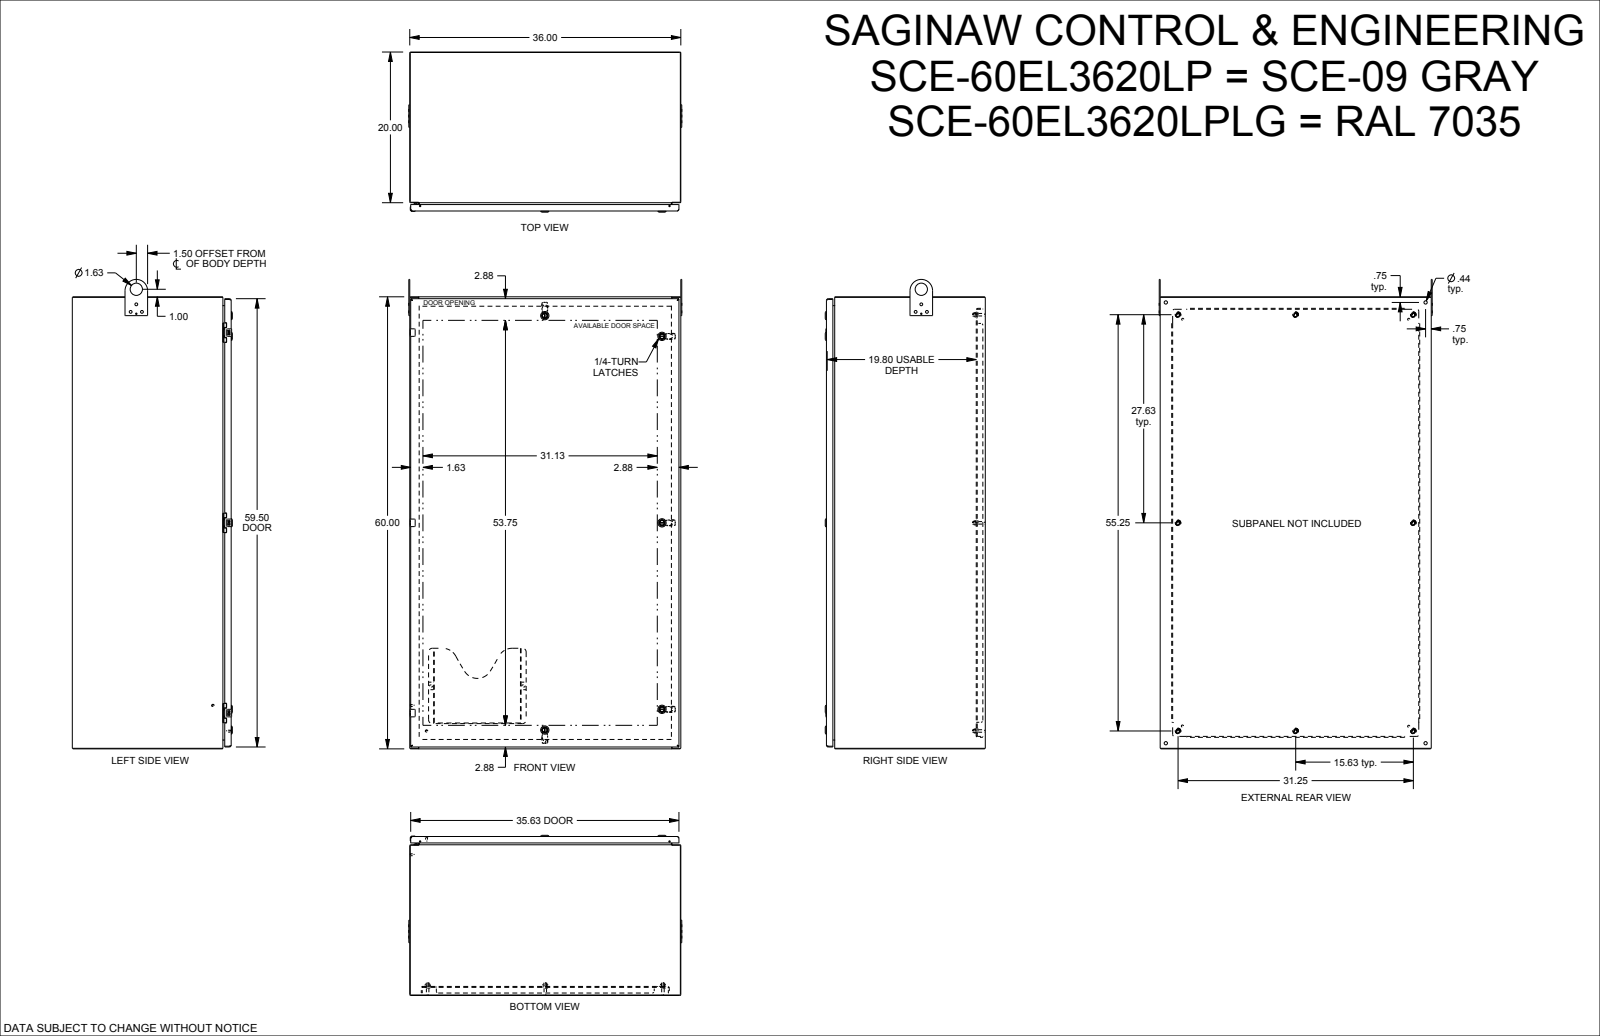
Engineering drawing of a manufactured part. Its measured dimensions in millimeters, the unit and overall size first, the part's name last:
Units: millimetres
Overall size (bounding box): 1582.7 × 921.1 × 558
Round holes (diameter × count): ⌀12.7 ×8, ⌀4.4 ×6, ⌀5.2 ×6, ⌀6.2 ×6, ⌀9.5 ×6, ⌀5 ×5, ⌀10 ×5, ⌀16.1 ×5, ⌀7.1 ×4, ⌀11.1 ×4, ⌀1 ×3, ⌀4.8 ×3
Round bosses / shafts (diameter × count): ⌀4.3 ×9, ⌀9.5 ×8, ⌀8.4 ×8, ⌀6.4 ×6, ⌀6.1 ×6, ⌀28 ×5, ⌀19.8 ×5, ⌀16 ×5
Partial cylindrical surfaces — rounded edges, fillets, slot ends (radius × count): R0.4 ×30, R4 ×20, R1 ×17, R6.6 ×16, R0.8 ×14, R0.8 ×12, R1.1 ×12, R1.6 ×12
Main face-to-face distances: 1.9, 912.5, 1.5, 535.9, 534, 534.3, 532.4, 28.6, 505.4, 27.3
Hole centre spacings: 641.4, 396.9, 440.1, 744.1, 806.1, 836.1, 1117.7, 1282.7
Volume: 15 150 000 mm³ · Surface area: 14 280 000 mm²
Bodies: 55 solids, 2465 faces (1206 planar, 871 cylindrical, 388 other)
Part name (STEP PRODUCT): SCE-60EL3620LP_REV2
STEP written by: SolidWorks 2021 (AUTOMOTIVE_DESIGN)
